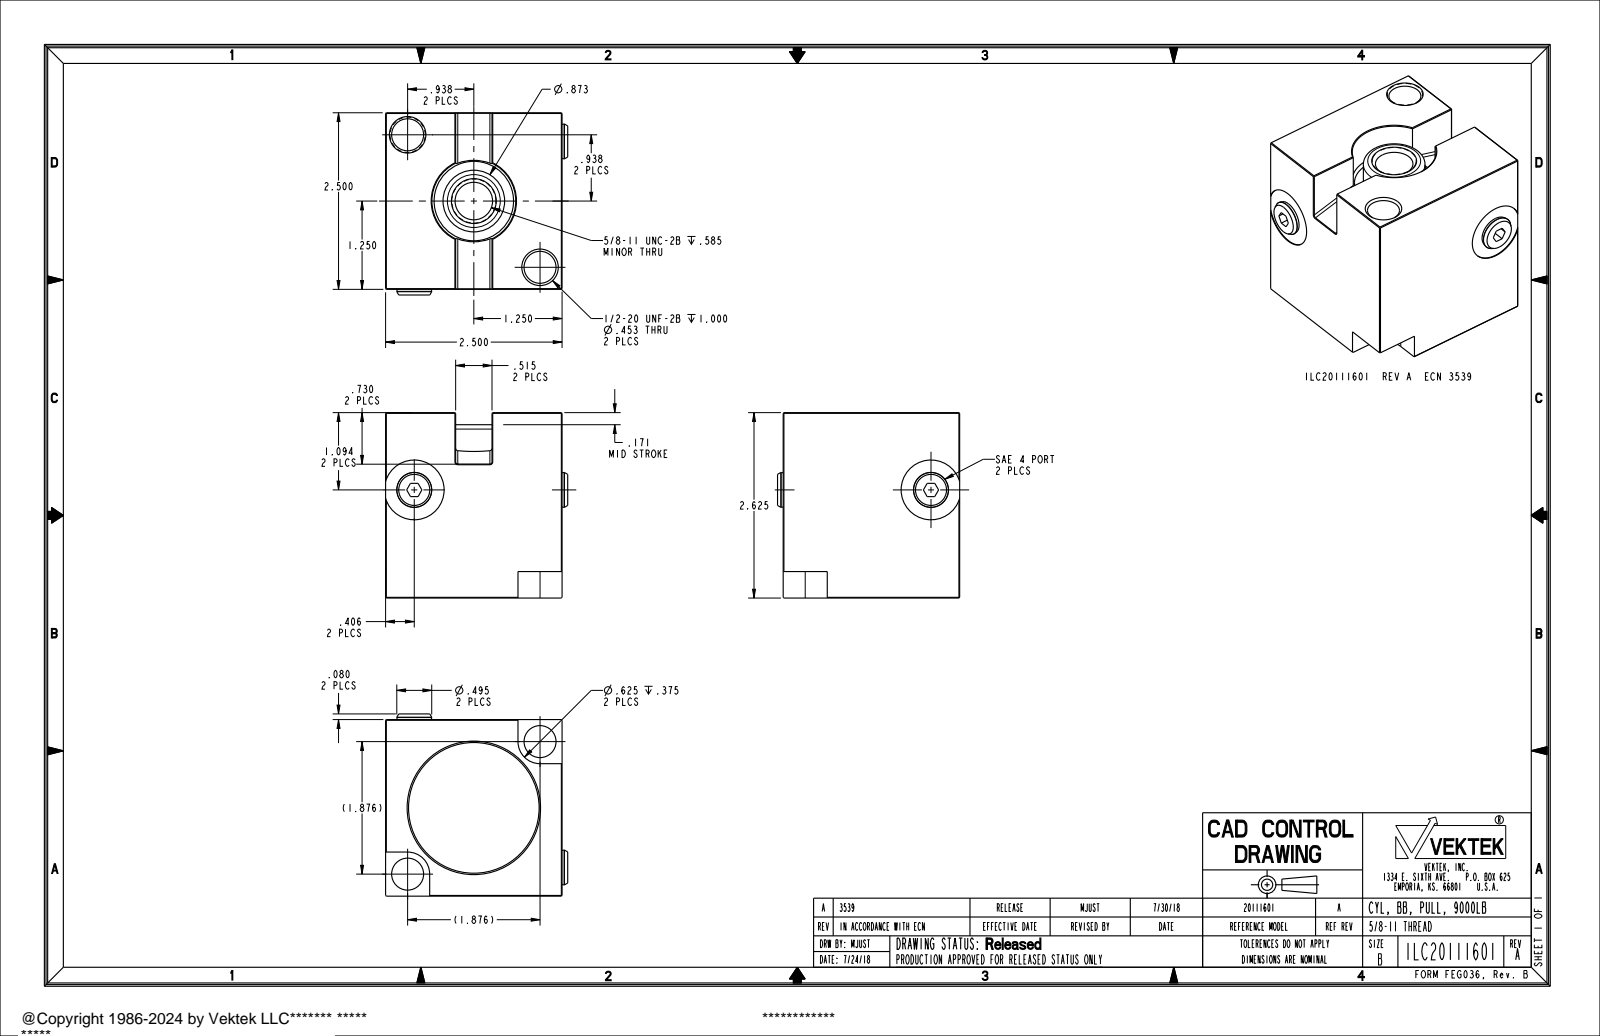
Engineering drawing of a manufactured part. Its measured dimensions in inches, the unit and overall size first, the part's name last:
Units: inches
Overall size (bounding box): 2.625 × 2.58 × 2.58
Round holes (diameter × count): ⌀0.453 ×2, ⌀0.846 ×2, ⌀0.581 ×1
Round bosses / shafts (diameter × count): ⌀0.5 ×2, ⌀1.125 ×1, ⌀0.873 ×1, ⌀0.625 ×1
Partial cylindrical surfaces — rounded edges, fillets, slot ends (radius × count): R0.03 ×4, R0.313 ×2, R0.594 ×1
Main face-to-face distances: 2.5, 2.605, 2.625, 0.02, 0.993, 1.507, 0.515, 2.49, 0.25, 2.375
Hole centre spacings: 1.327, 2.654
Volume: 14.43 in³ · Surface area: 53.95 in²
Bodies: 1 solid, 125 faces (69 planar, 26 cylindrical, 30 other)
Part name (STEP PRODUCT): ILC20111601
STEP written by: PRO/ENGINEER BY PARAMETRIC TECHNOLOGY CORPORATION, 2013320 (AUTOMOTIVE_DESIGN)
